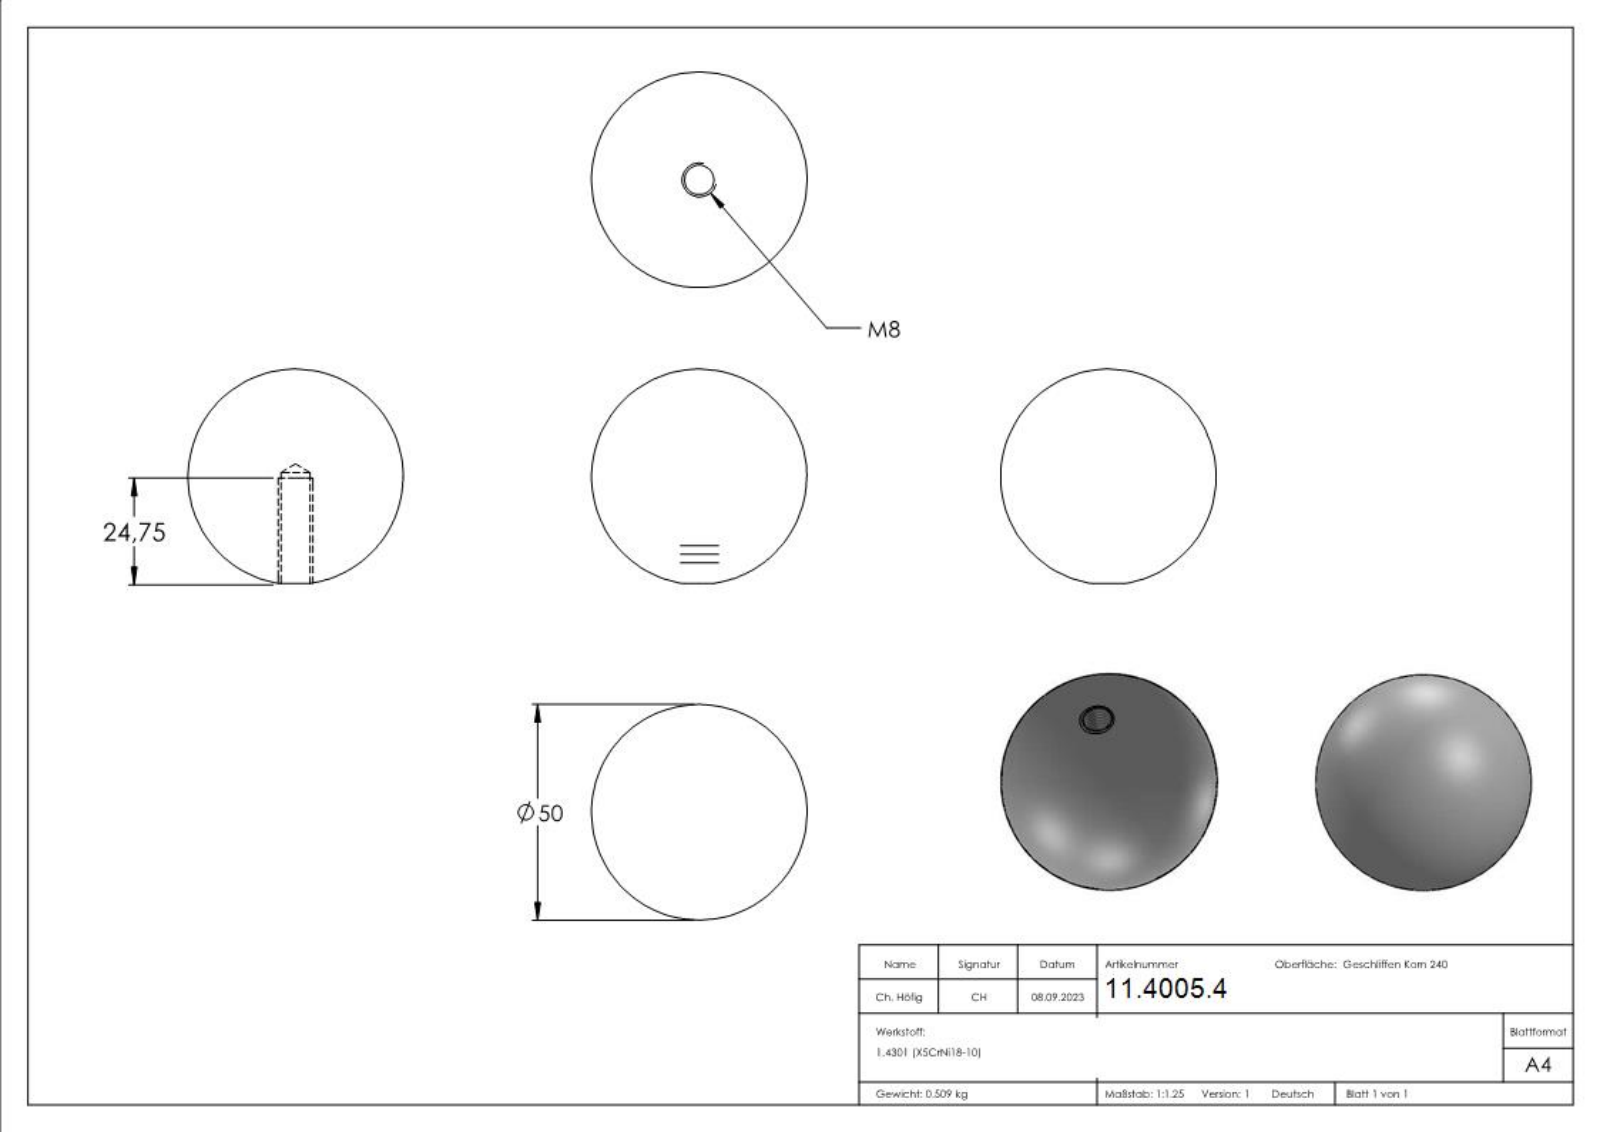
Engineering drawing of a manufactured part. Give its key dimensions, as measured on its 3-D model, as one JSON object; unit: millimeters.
{"part_name": "51050-240", "step_written_by": "SolidWorks 2018 (CONFIG_CONTROL_DESIGN)", "units": "millimeters", "bodies": {"solids": 1, "faces": 3, "planar": 0, "cylindrical": 1, "other": 2}, "overall_size": [50, 50, 49.77], "volume_mm3": 64485, "surface_area_mm2": 8410, "round_holes": [[6.8, 1]]}
